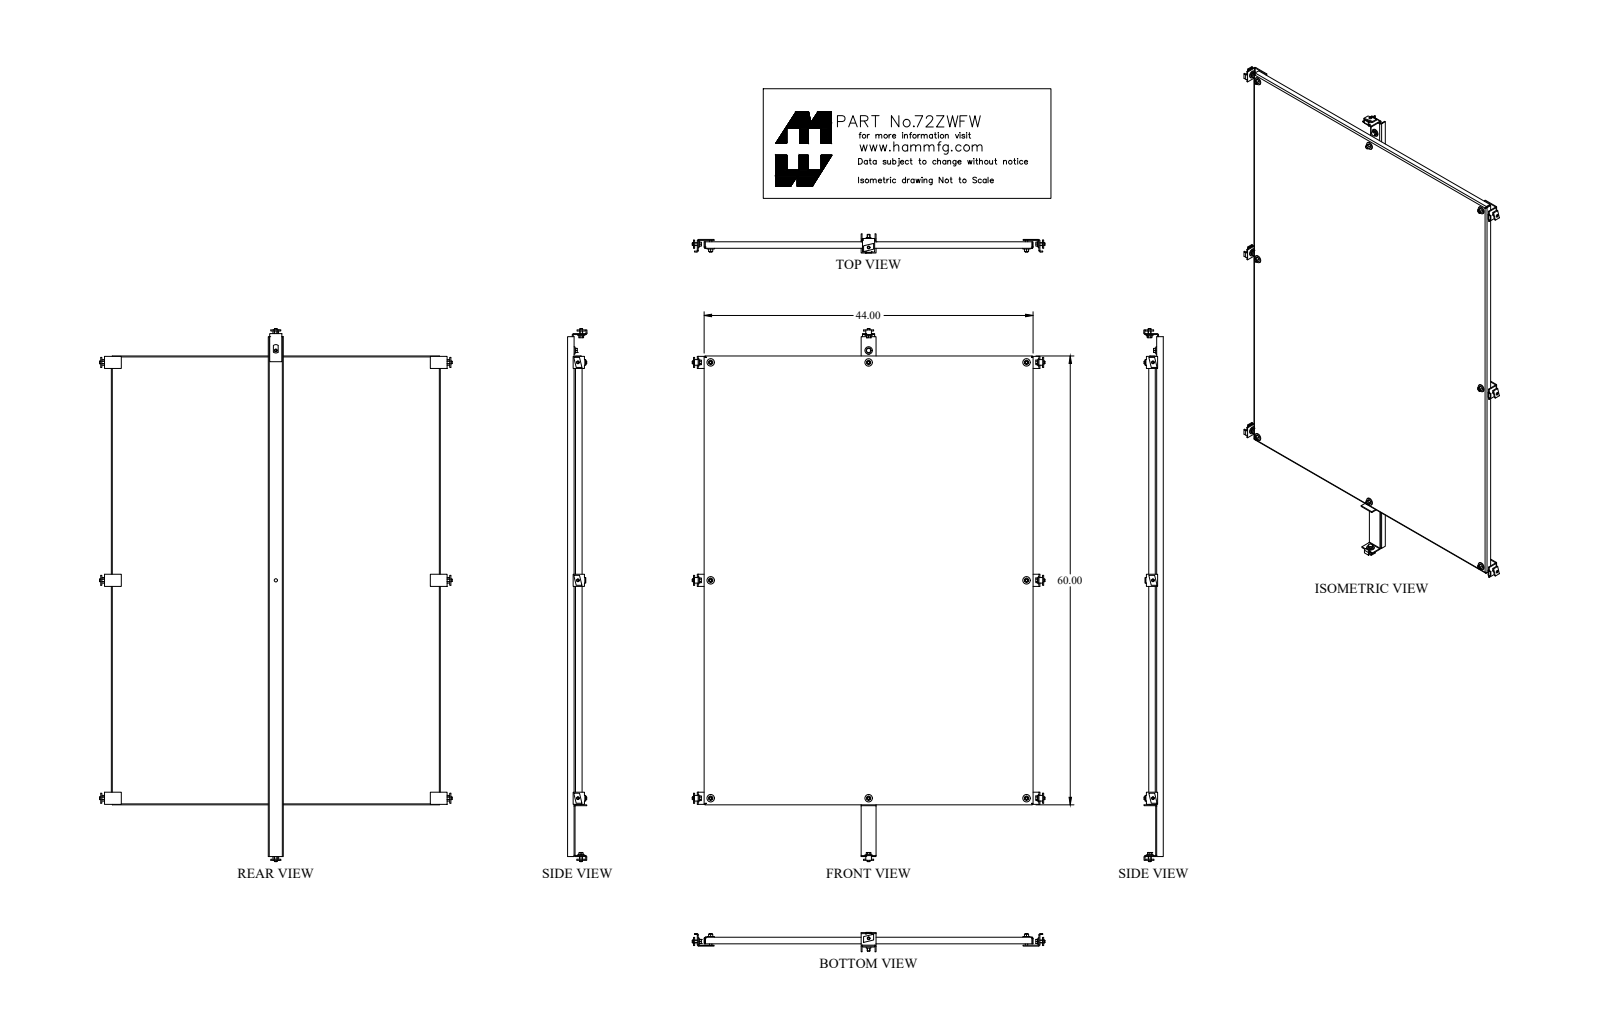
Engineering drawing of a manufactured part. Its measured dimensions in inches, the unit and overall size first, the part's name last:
Units: inches
Overall size (bounding box): 60 × 44 × 0.875
Round holes (diameter × count): ⌀0.563 ×8
Partial cylindrical surfaces — rounded edges, fillets, slot ends (radius × count): R0.06 ×4, R0.185 ×4
Main face-to-face distances: 0.125, 43.875, 59.875, 44, 43.75, 60, 59.75, 0.875, 0.75, 0.125
Hole centre spacings: 21.125, 29.125, 35.979, 51.315, 61.962, 42.25, 58.25, 71.959
Volume: 347.8 in³ · Surface area: 5 593 in²
Bodies: 1 solid, 70 faces (38 planar, 24 cylindrical, 8 other)
Part name (STEP PRODUCT): 72ZWFW_Default
STEP written by: SolidWorks 2018 (CONFIG_CONTROL_DESIGN)
